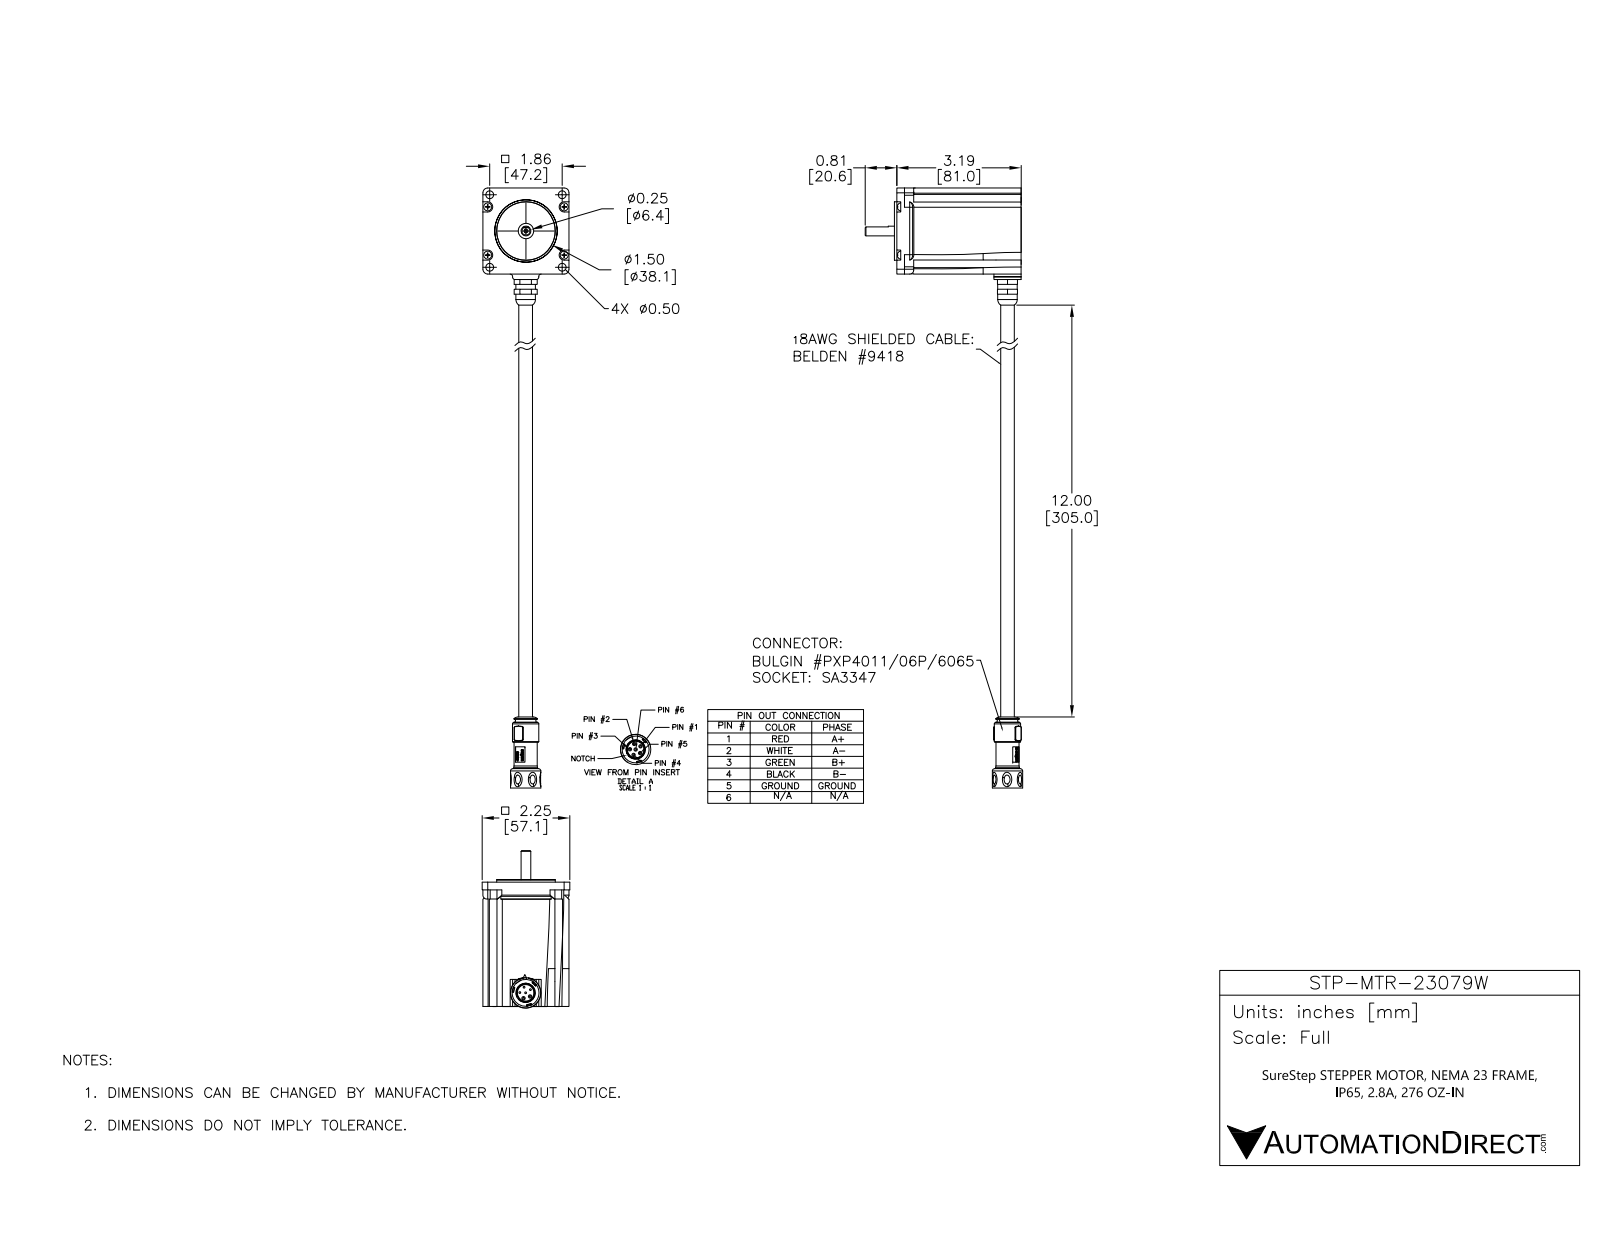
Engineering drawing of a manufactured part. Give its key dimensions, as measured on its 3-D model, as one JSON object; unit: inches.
{"part_name": "STP-MTR-23079W", "step_written_by": "SolidWorks 2017 (AUTOMOTIVE_DESIGN)", "units": "inches", "bodies": {"solids": 3, "faces": 897, "planar": 365, "cylindrical": 233, "other": 299}, "overall_size": [15.376, 4.036, 2.207], "volume_in3": 14.54, "surface_area_in2": 73.25, "round_holes": [[0.047, 6], [0.097, 4], [0.2, 4], [0.125, 3], [0.125, 2], [0.063, 1], [0.228, 1], [0.394, 1], [0.398, 1], [0.449, 1], [0.467, 1], [0.689, 1]], "round_bosses_or_shafts": [[0.05, 4], [1.7, 1], [1.5, 1], [0.777, 1], [0.674, 1], [0.613, 1], [0.592, 1], [0.5, 1]], "partial_cylinders_radius": [[0.005, 28], [0.02, 12], [0.125, 10], [0.388, 6], [0.062, 4], [0.129, 4], [0.175, 4], [0.196, 4]], "face_to_face_distances": [2.207, 0.314, 2.014, 1.7, 1.171, 1.485, 3.185, 1.174, 1.487, 3.187], "hole_center_spacings": [0.147, 0.148, 0.281, 0.316, 1.181, 1.553, 1.649, 1.661]}
